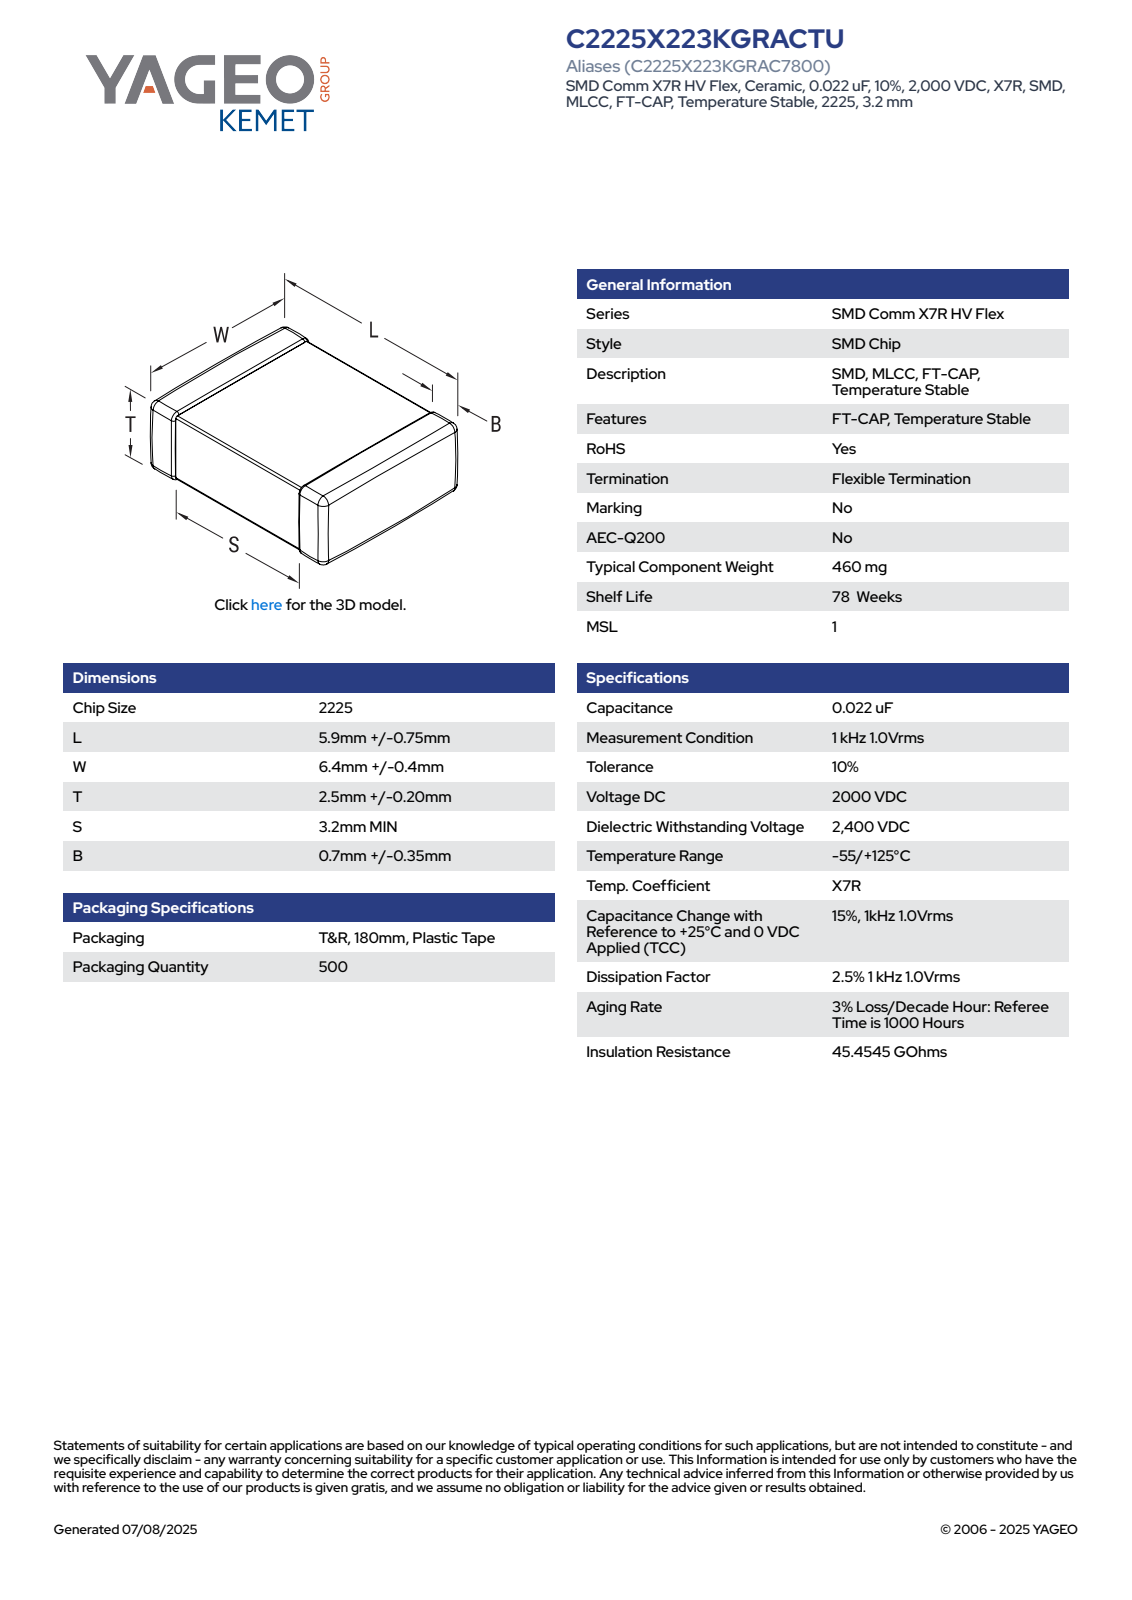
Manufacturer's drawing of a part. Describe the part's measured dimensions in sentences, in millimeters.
The part is named "CCS_CCSTD_2225_L6.65W6.8T2.7B0.7". Its 3-D file was written by "SolidWorks 2021 (AUTOMOTIVE_DESIGN)". It is 4 solids with 125 faces: 71 planar, 38 cylindrical and 16 other. Overall it measures 6.8 by 6.65 by 2.7 millimeters. Its volume is 110 cubic millimeters and its surface area 163 square millimeters. Partial cylindrical surfaces (rounded edges, fillets, slot ends): 24 of radius 0.14. The main face-to-face distances are 2.42, 2.56, 6.65, 2.7, 6.52, 6.66, 6.8, 1, 2.59, 4.06.
